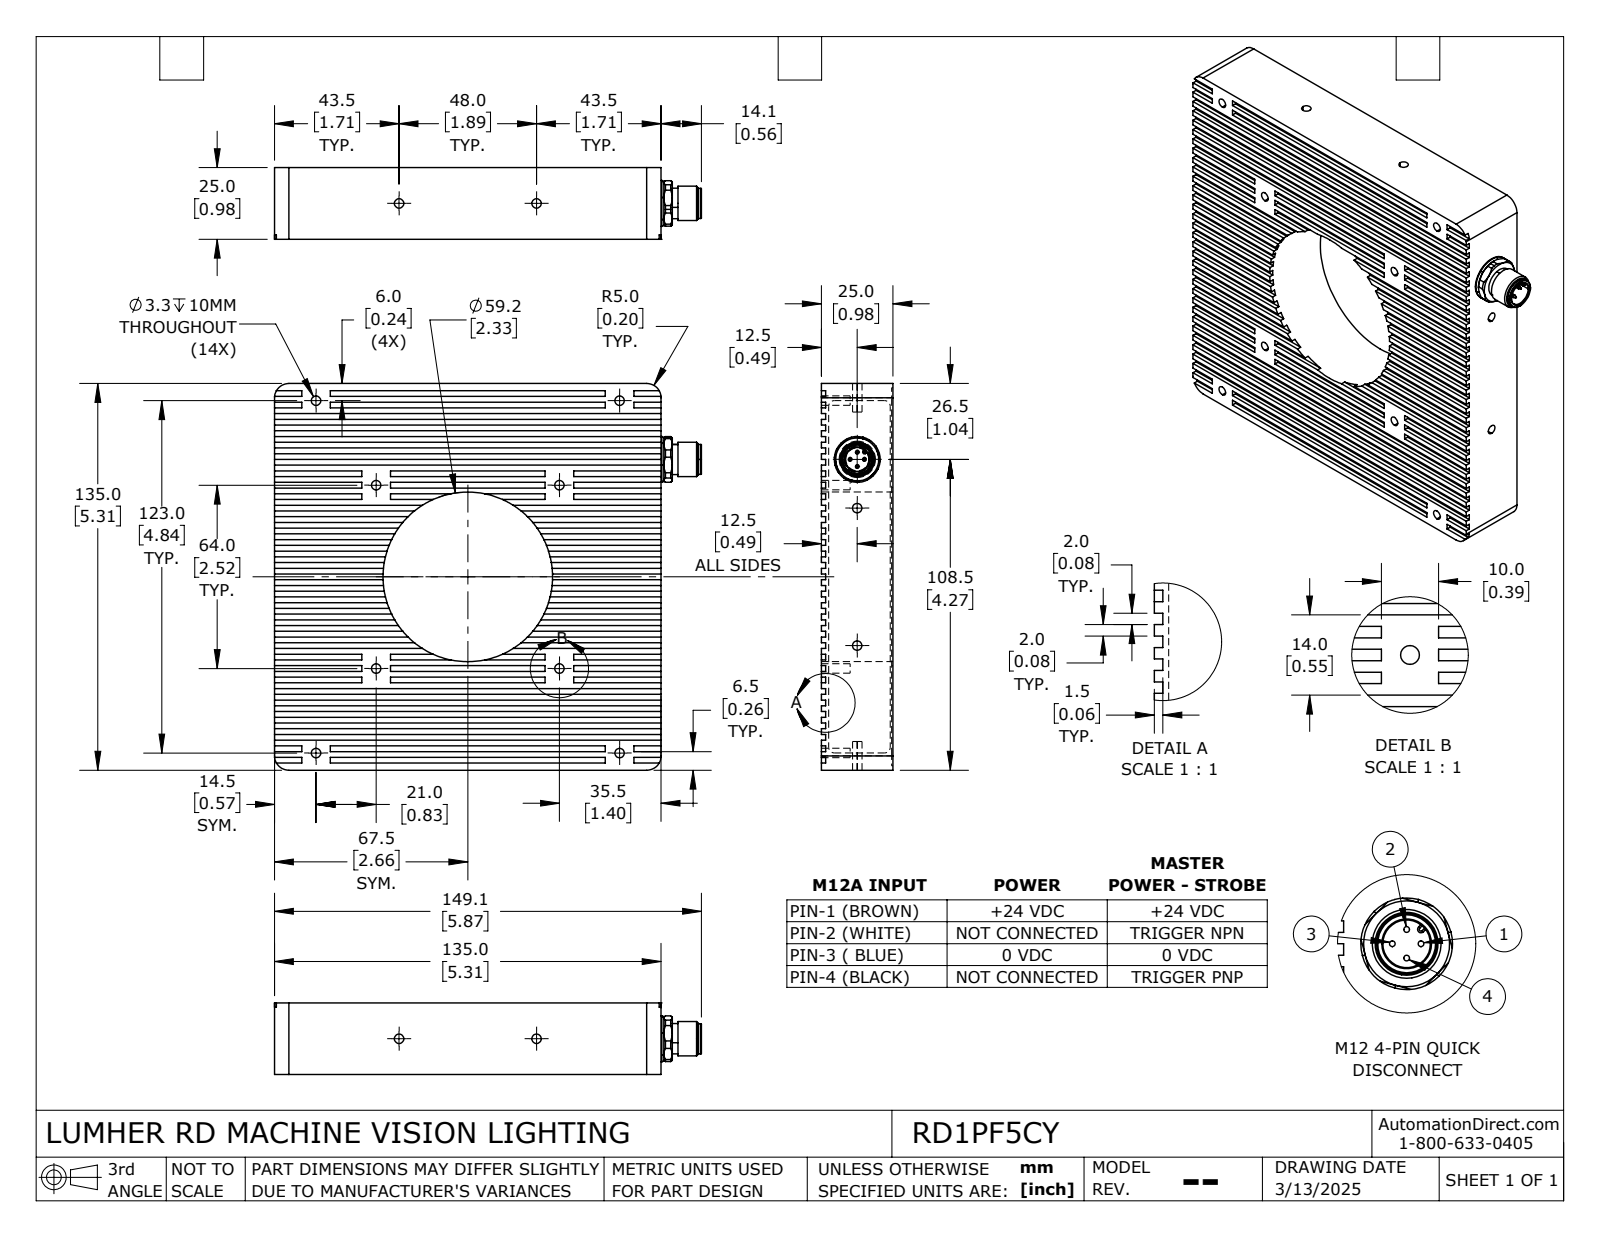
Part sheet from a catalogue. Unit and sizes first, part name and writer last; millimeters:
Units: millimetres
Overall size (bounding box): 149.1 × 135 × 25
Round holes (diameter × count): ⌀3.3 ×12, ⌀1.45 ×4, ⌀8.3 ×1, ⌀9.4 ×1, ⌀59.2 ×1
Round bosses / shafts (diameter × count): ⌀1.4 ×4, ⌀1 ×4, ⌀62.2 ×1, ⌀16 ×1, ⌀12 ×1, ⌀11.9 ×1, ⌀10.6 ×1, ⌀10.5 ×1
Partial cylindrical surfaces — rounded edges, fillets, slot ends (radius × count): R2 ×4, R3.5 ×4, R5 ×4, R0.3 ×2, R0.6 ×1
Main face-to-face distances: 24.5, 1.5, 23, 135, 2, 4, 134.6, 6, 8, 10
Hole centre spacings: 2.5, 3.54, 36.21, 45.25, 64, 81.19, 89.97, 95.83
Volume: 367 454 mm³ · Surface area: 62 778 mm²
Bodies: 1 solid, 578 faces (346 planar, 133 cylindrical, 99 other)
Part name (STEP PRODUCT): RD1PD5CY
STEP written by: SolidWorks 2024 (AUTOMOTIVE_DESIGN)
